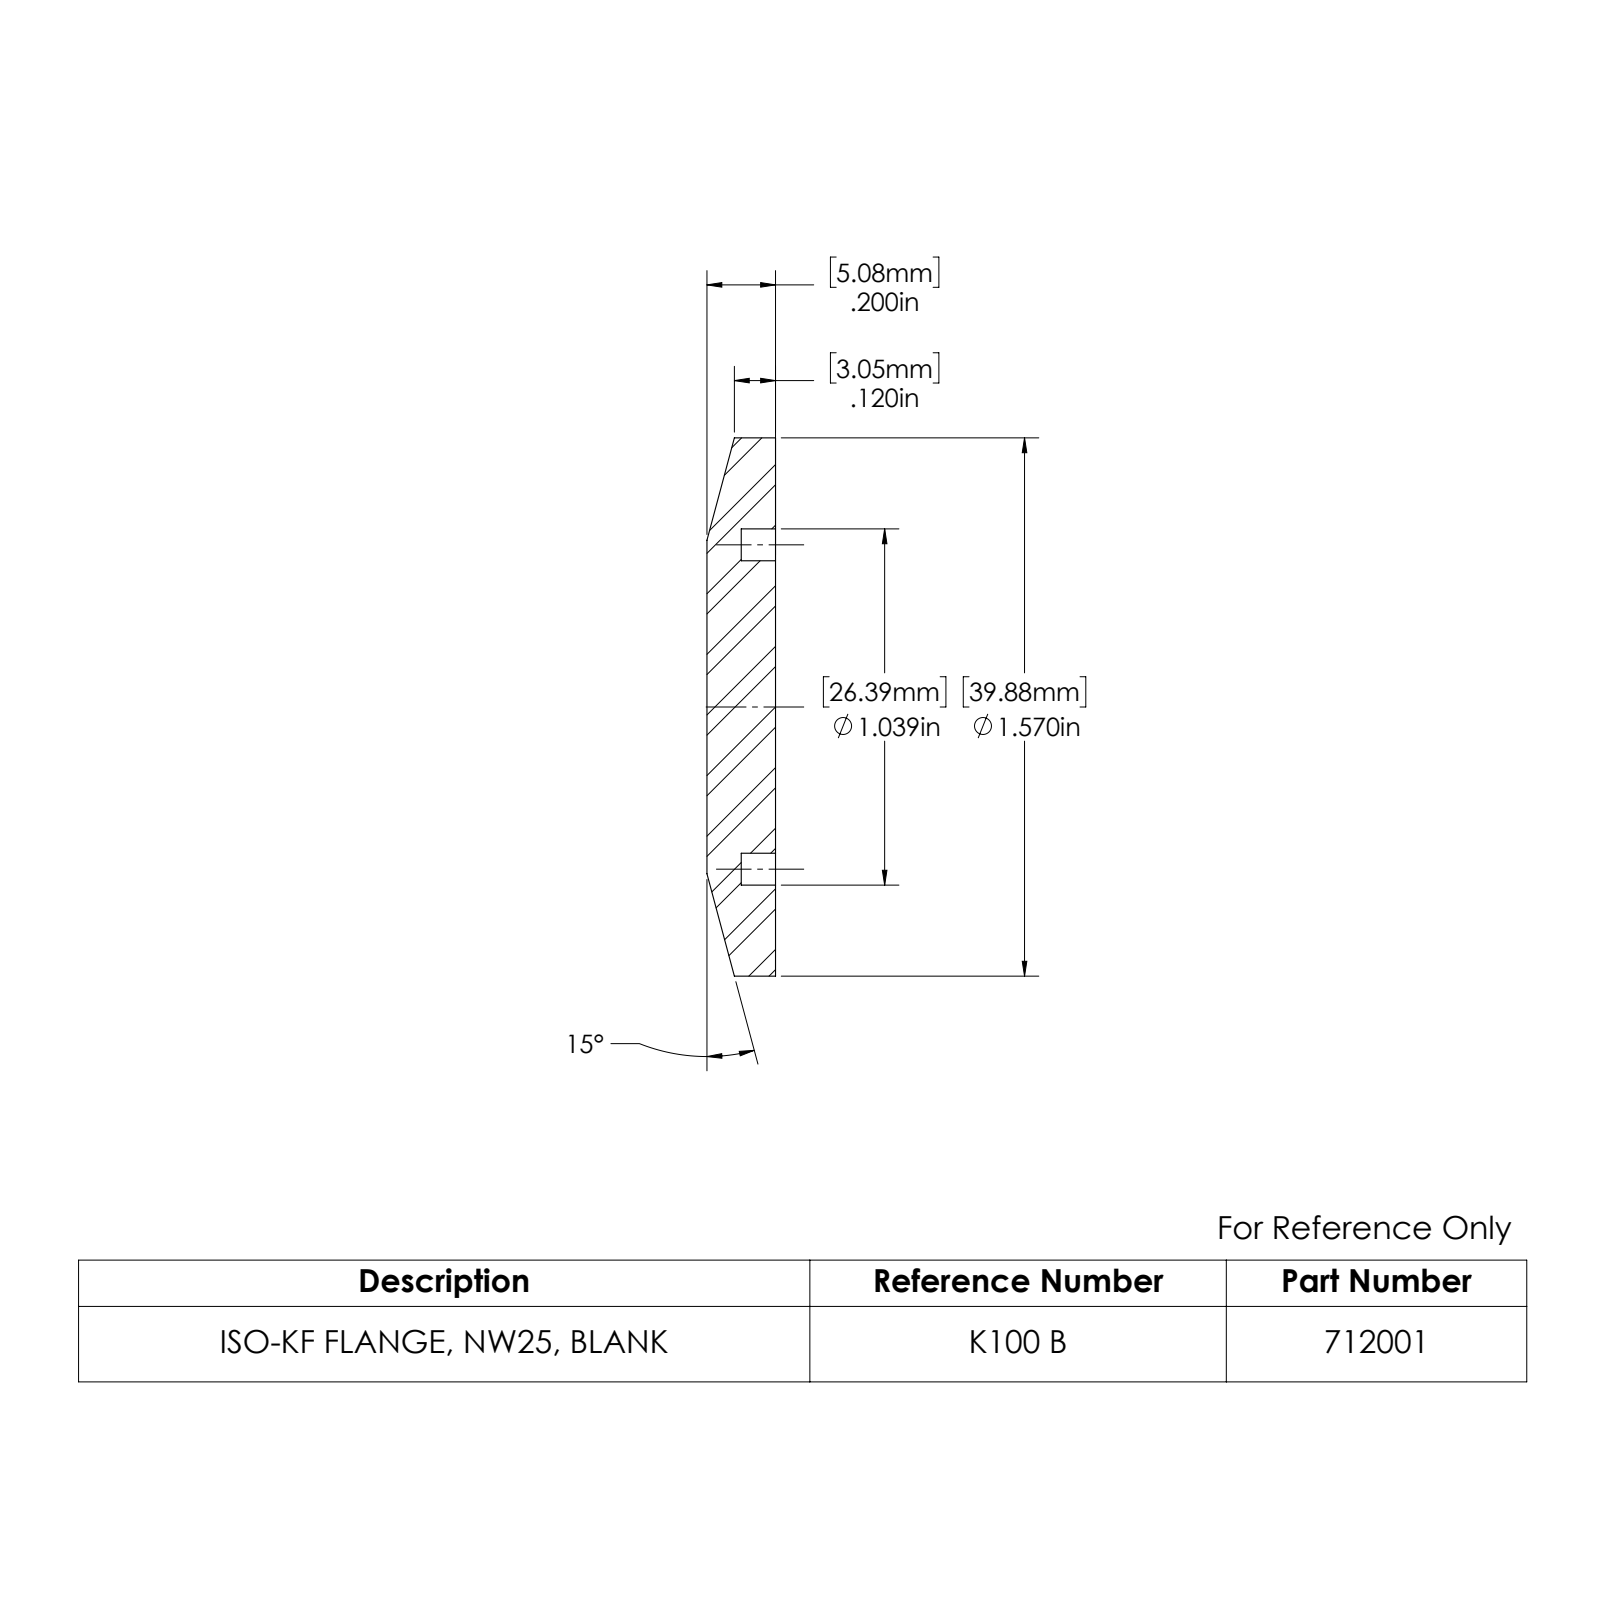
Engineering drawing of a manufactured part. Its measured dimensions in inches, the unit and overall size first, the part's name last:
Units: inches
Overall size (bounding box): 1.57 × 1.57 × 0.2
Round holes (diameter × count): ⌀1.039 ×1
Round bosses / shafts (diameter × count): ⌀1.57 ×1, ⌀0.853 ×1
Main face-to-face distances: 0.2, 0.1
Volume: 0.308 in³ · Surface area: 5.065 in²
Bodies: 1 solid, 16 faces (4 planar, 6 cylindrical, 6 other)
Part name (STEP PRODUCT): 712001
STEP written by: SolidWorks 2022 (AUTOMOTIVE_DESIGN)
